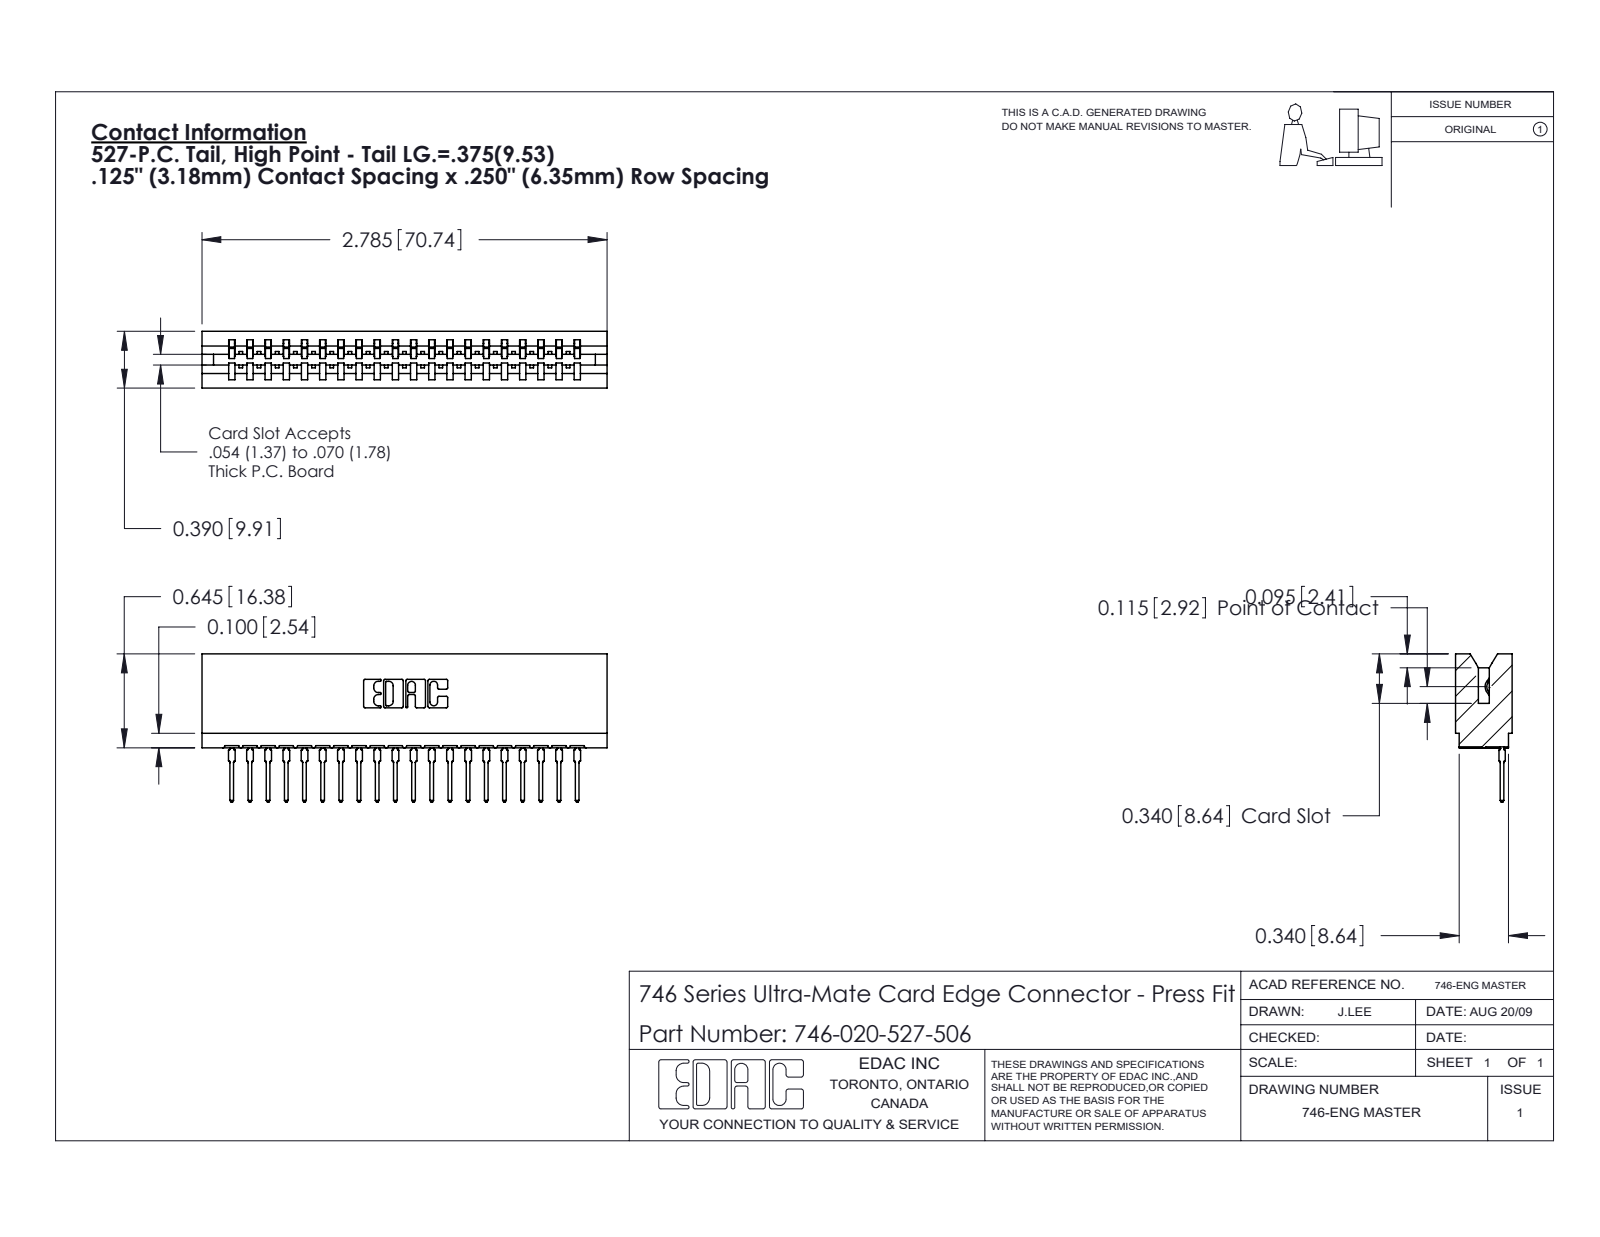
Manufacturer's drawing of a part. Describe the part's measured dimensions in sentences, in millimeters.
The part is named "746 Part_.340 Slot Depth - 06; 746-292-001_527; 746-020-527-506". Its 3-D file was written by "SolidWorks 2020 (CONFIG_CONTROL_DESIGN)". It is 21 solids with 2258 faces: 1316 planar, 422 cylindrical and 520 other. Overall it measures 70.7 by 25.9 by 9.9 millimeters. Its volume is 8 080 cubic millimeters and its surface area 10 680 square millimeters. Partial cylindrical surfaces (rounded edges, fillets, slot ends): 40 of radius 0.5, 22 of radius 0.3, 21 of radius 0.4, 6 of radius 0.2, 6 of radius 0.8, 4 of radius 0.1, 4 of radius 0.3, 3 of radius 0.7. The main face-to-face distances are 6.4, 1.4, 8.5, 9.9, 12.7, 3.2, 0.6, 7.8, 1.1, 3.2.
